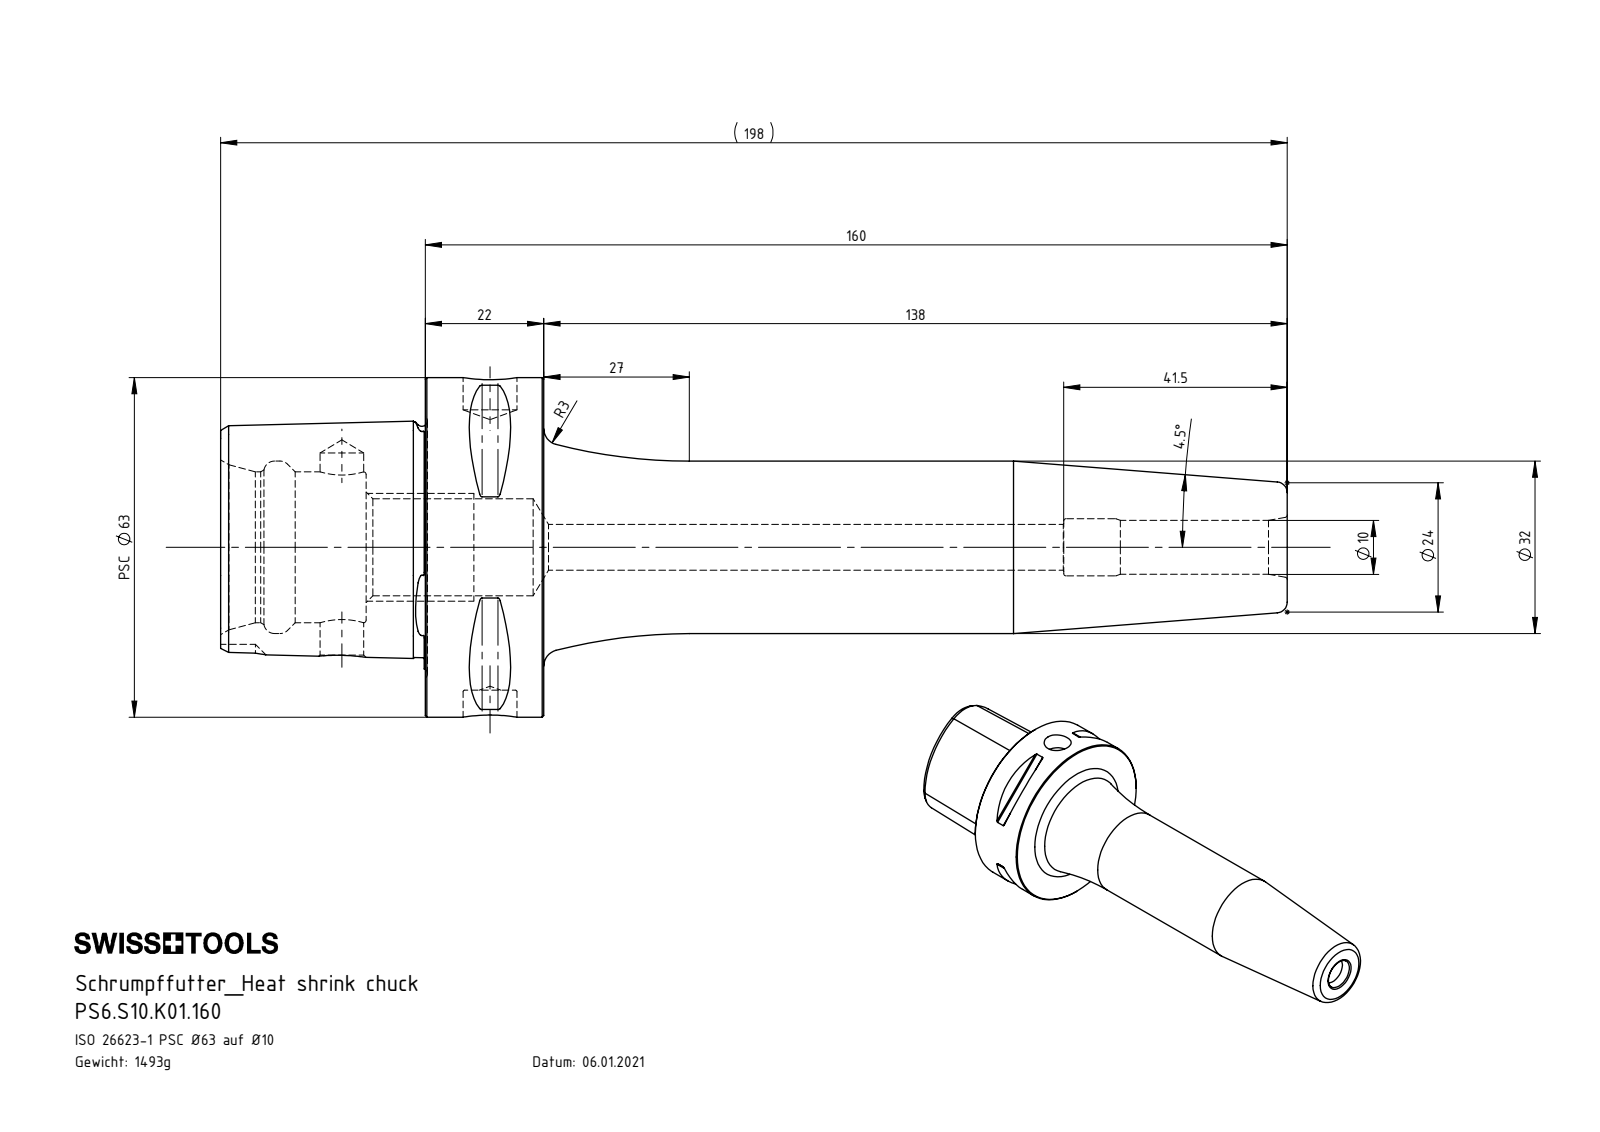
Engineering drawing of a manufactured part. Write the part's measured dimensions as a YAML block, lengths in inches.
part_name: "PS6.S10.K01.160"
step_written_by: "SolidWorks 2022 (AUTOMOTIVE_DESIGN)"
units: inches
bodies: {solids: 1, faces: 154, planar: 22, cylindrical: 35, other: 97}
overall_size: [7.795, 2.48, 2.48]
volume: 11.6
surface_area: 57.14
round_holes:
  - {diameter: 0.394, count: 2}
  - {diameter: 0.319, count: 1}
  - {diameter: 0.335, count: 1}
  - {diameter: 0.417, count: 1}
  - {diameter: 0.709, count: 1}
  - {diameter: 1.102, count: 1}
  - {diameter: 1.26, count: 1}
round_bosses_or_shafts:
  - {diameter: 2.48, count: 1}
partial_cylinders:
  - {radius: 0.02, count: 8}
  - {radius: 0.236, count: 1}
face_to_face_distances: [0.866, 1.496, 2.362, 0.98, 1.063, 0.433, 1.299, 7.795, 6.732, 6.299]
hole_center_spacings: [1.083]
